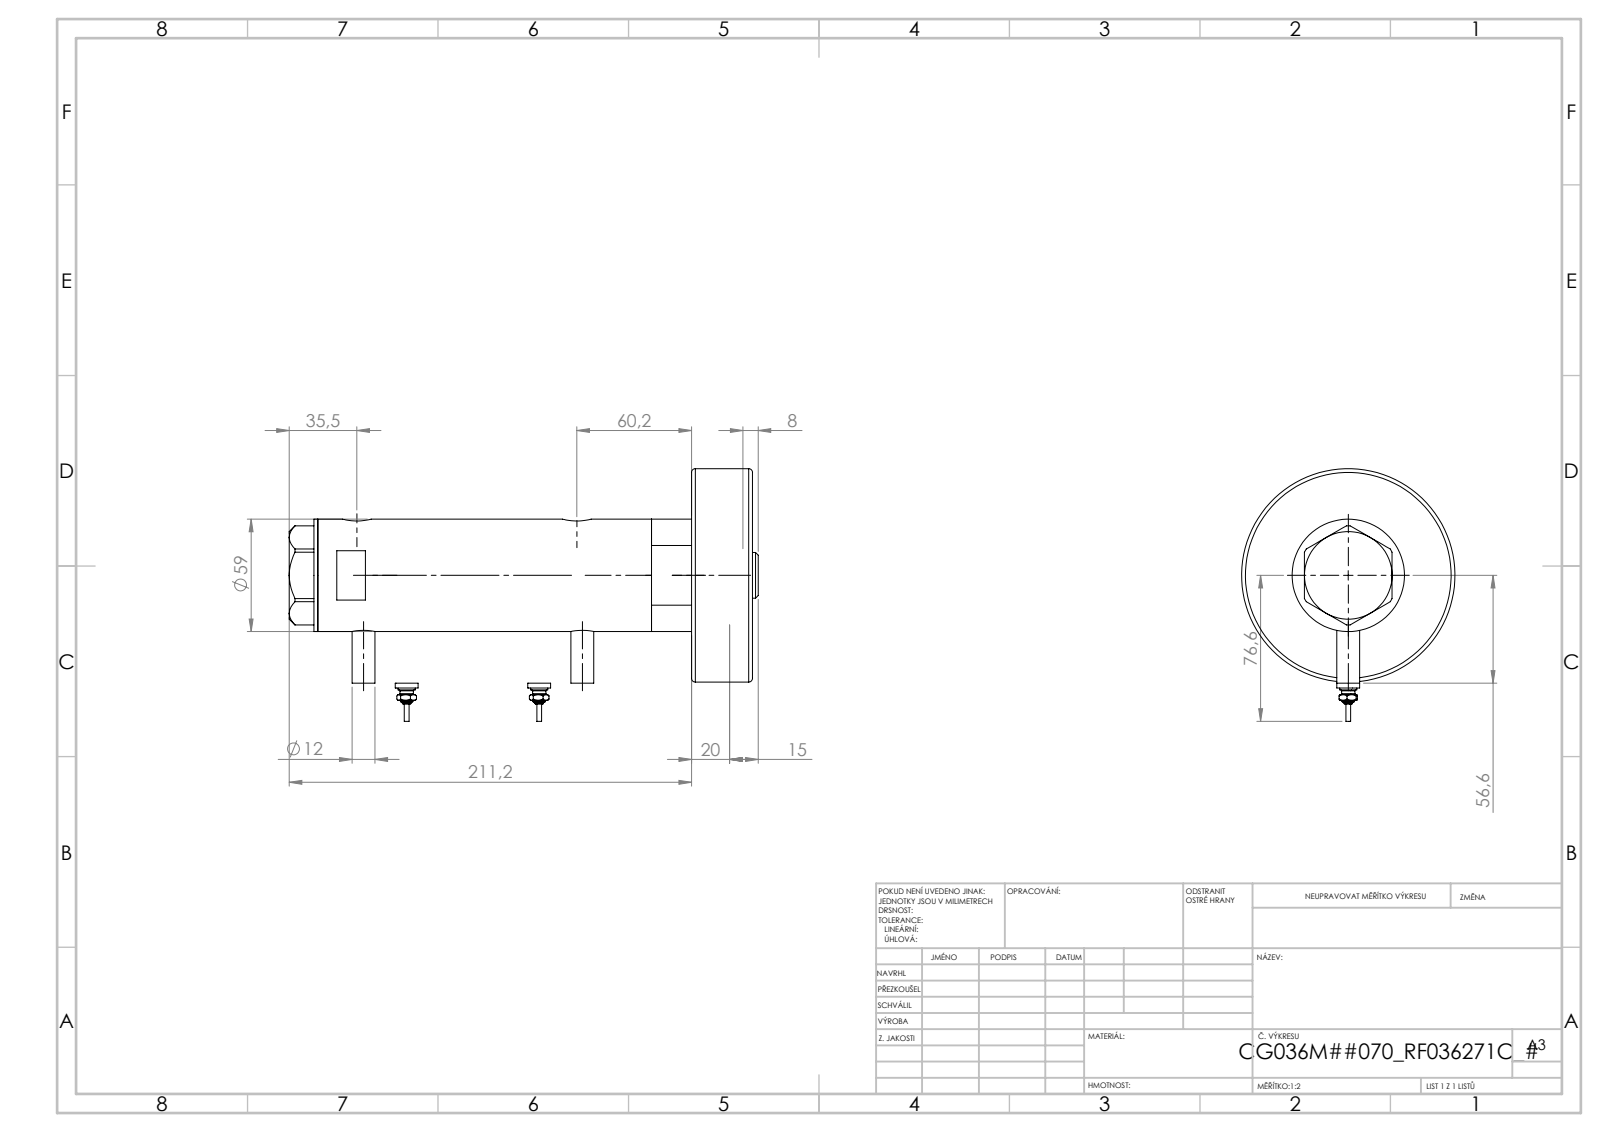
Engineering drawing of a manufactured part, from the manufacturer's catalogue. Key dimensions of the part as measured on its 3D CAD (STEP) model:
Part name (STEP PRODUCT): V270CG_BACK; V270CG_FRONT; V270CG_SWITCH; V270CG_271C (+2 more)
STEP written by: SolidWorks 2019 (CONFIG_CONTROL_DESIGN)
Units: millimetres
Bodies: 7 solids, 242 faces (83 planar, 81 cylindrical, 78 other)
Overall size (bounding box): 233.42 × 117.8 × 112
Volume: 785 246 mm³ · Surface area: 141 791 mm²
Round holes (diameter × count): ⌀5 ×2, ⌀9.73 ×2, ⌀12.5 ×2, ⌀15 ×2, ⌀8.5 ×1, ⌀25 ×1, ⌀26.5 ×1, ⌀36 ×1, ⌀40 ×1, ⌀48 ×1, ⌀52 ×1
Round bosses / shafts (diameter × count): ⌀12 ×4, ⌀9 ×2, ⌀7 ×2, ⌀4.34 ×2, ⌀2.4 ×2, ⌀112 ×1, ⌀59 ×1, ⌀46 ×1
Main face-to-face distances: 32.01, 180.84, 212.85, 127.34, 53.5, 85.51, 23.5, 103.84, 157.34, 189.35
Hole centre spacings: 2.9, 3.5, 102.15, 105.05, 105.65, 108.55, 2.89, 2.91
